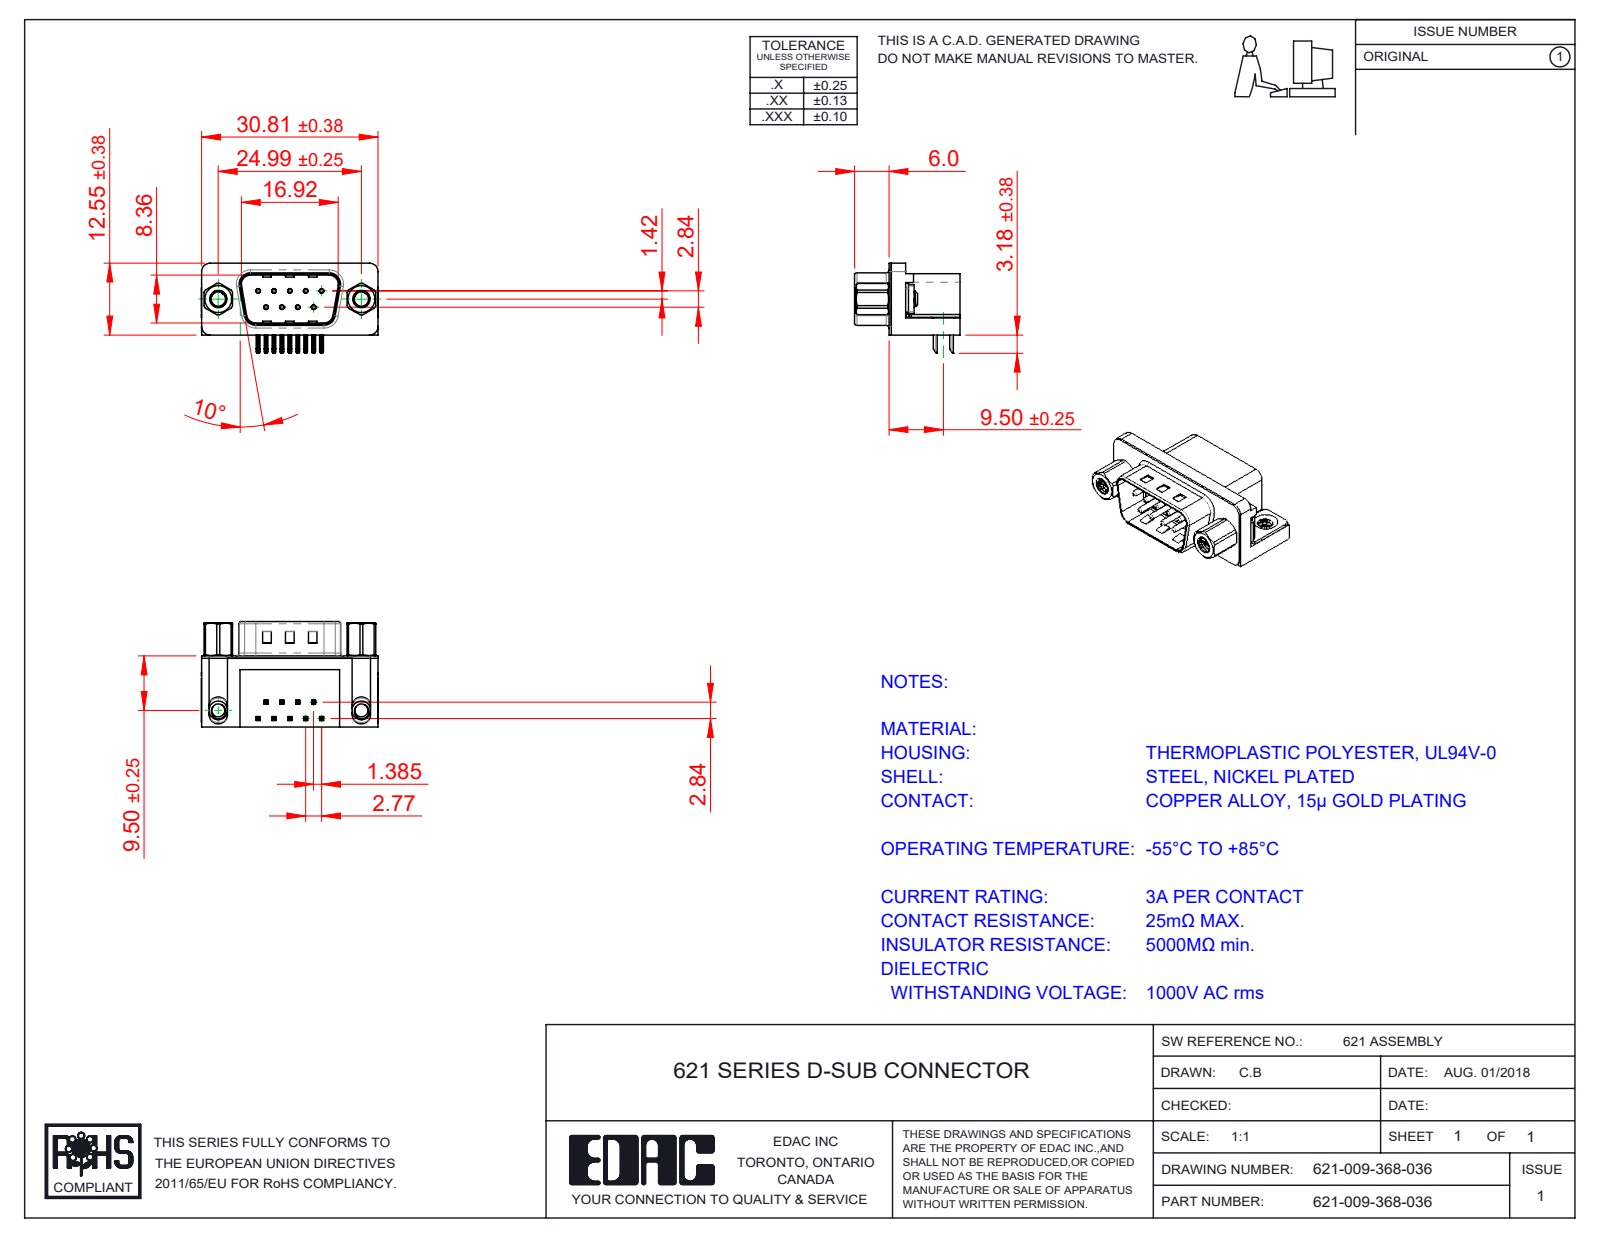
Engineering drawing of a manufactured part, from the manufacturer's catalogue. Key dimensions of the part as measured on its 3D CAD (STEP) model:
Part name (STEP PRODUCT): 621 Contact Bottom; 621 Shell_9 Socket; 621 2 Prong Board Lock; 621 M3 Threaded Rivet (+4 more)
STEP written by: SolidWorks 2016 (CONFIG_CONTROL_DESIGN)
Units: millimetres
Bodies: 17 solids, 1179 faces (627 planar, 419 cylindrical, 133 other)
Overall size (bounding box): 30.89 × 18.4 × 16.25
Volume: 3 485 mm³ · Surface area: 4 959 mm²
Round holes (diameter × count): ⌀0.35 ×9, ⌀0.8 ×9, ⌀2.5 ×2, ⌀4 ×2, ⌀4.8 ×2, ⌀5 ×2
Round bosses / shafts (diameter × count): ⌀0.75 ×9, ⌀4.9 ×2, ⌀4.75 ×2, ⌀3.9 ×2, ⌀3 ×2
Partial cylindrical surfaces — rounded edges, fillets, slot ends (radius × count): R0.25 ×44, R0.12 ×18, R1 ×16, R0.5 ×14, R1.5 ×8, R1.6 ×8, R0.32 ×4, R0.9 ×4
Main face-to-face distances: 0.4, 12, 12.4, 10.35, 0.5, 9.5, 2.5, 2.9, 2.1, 0.35
Hole centre spacings: 3.16, 2.77, 5.54, 5.03, 5.04, 8.31, 7.48, 7.49
